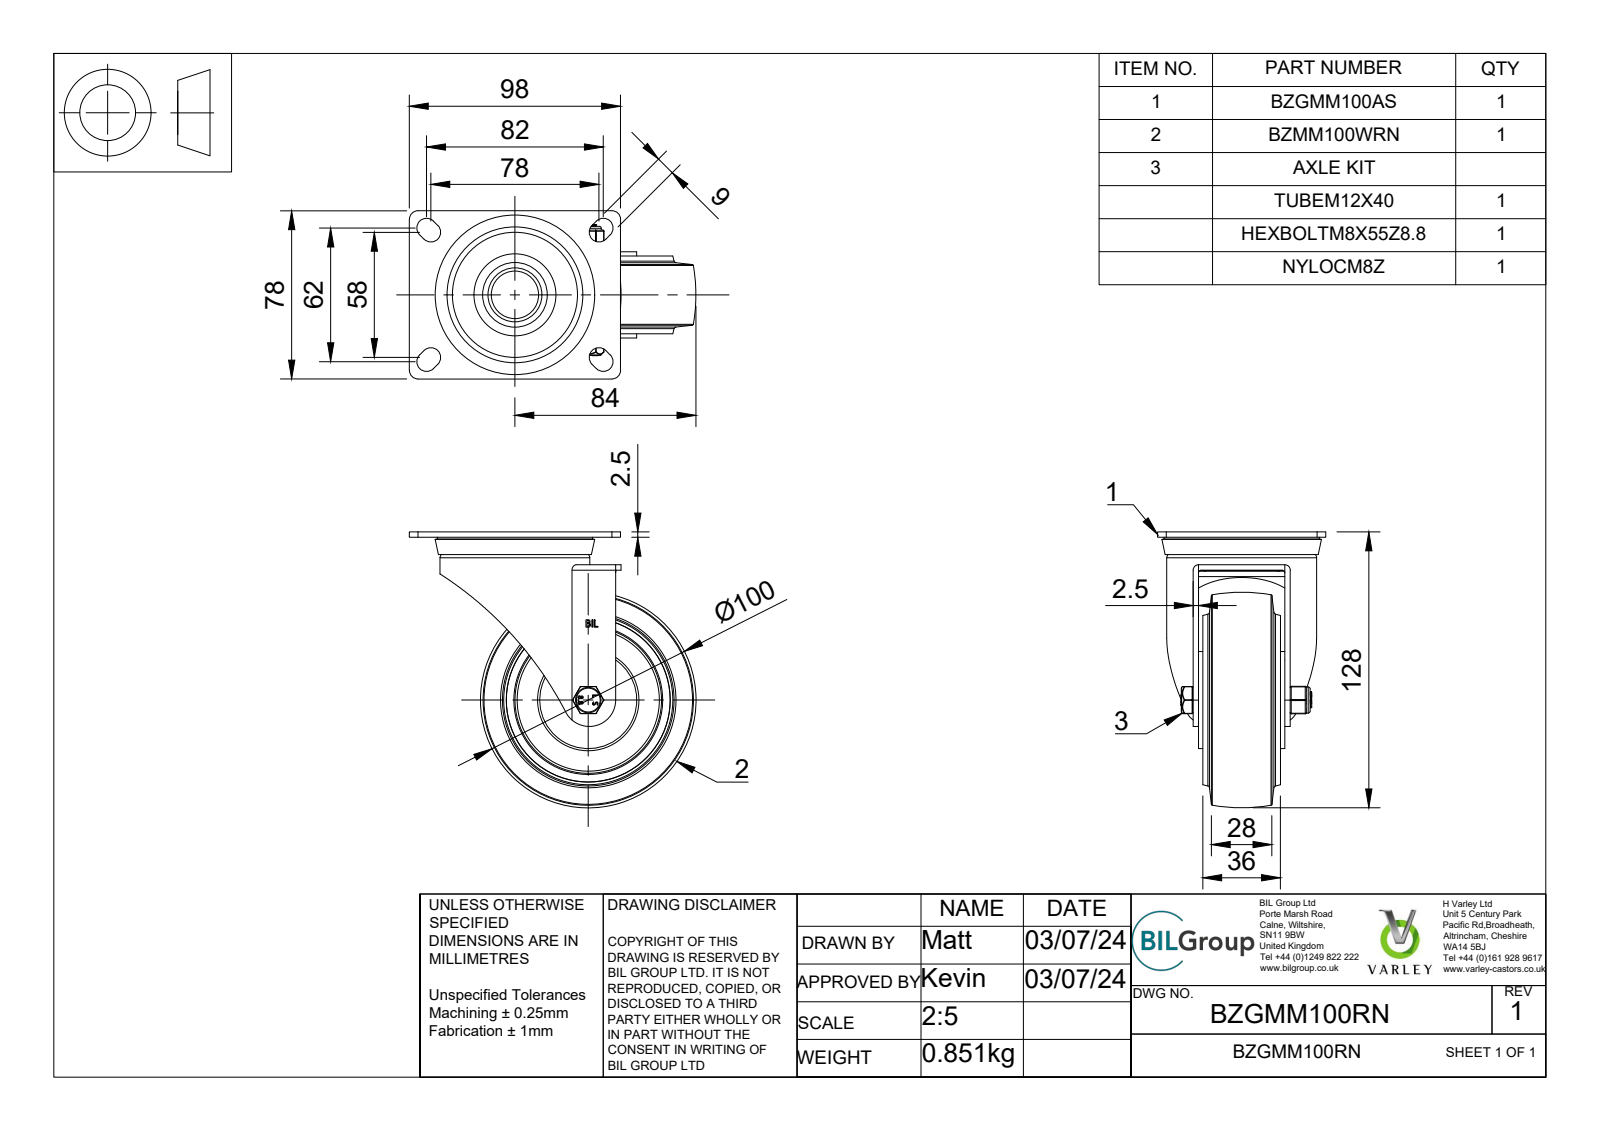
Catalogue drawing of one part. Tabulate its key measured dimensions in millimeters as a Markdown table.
| quantity | value |
| --- | --- |
| part name | BZGMM100RN v3; BZGMM100AS - 2 v1; ZINC PLATED, PRESSED STEEL TOP PLATE; ZINC PLATED, PRESSED STEEL TOP PLATE Geometry (+7 more) |
| STEP written by | Autodesk Translation Framework v13.14.0.145 (AUTOMOTIVE_DESIGN) |
| units | millimeters |
| bodies | 37 solids, 388 faces (124 planar, 138 cylindrical, 126 other) |
| overall size | 133 × 128 × 78 |
| volume | 297 971 mm³ |
| surface area | 111 480 mm² |
| round holes (diameter × count) | 0.66 × 2, 8 × 1, 8.2 × 1, 8.4 × 1, 8.6 × 1, 12.2 × 1, 26 × 1, 30 × 1, 64.5 × 1, 68 × 1, 76 × 1 |
| round bosses / shafts (diameter × count) | 69.5 × 1, 47 × 1, 45 × 1, 25 × 1, 12.1 × 1, 11.9 × 1, 11.5 × 1, 7.87 × 1 |
| partial cylindrical surfaces (radius × count) | 0.5 × 18, 0.25 × 12, 4.5 × 8, 0.33 × 4, 0.64 × 4, 1.25 × 4, 4 × 4, 0.63 × 2 |
| main face-to-face distances | 2.5, 13, 27, 4.5, 40, 15.5, 29.5, 42.5, 2, 3 |
| hole center spacings | 3.22, 2.49 |
